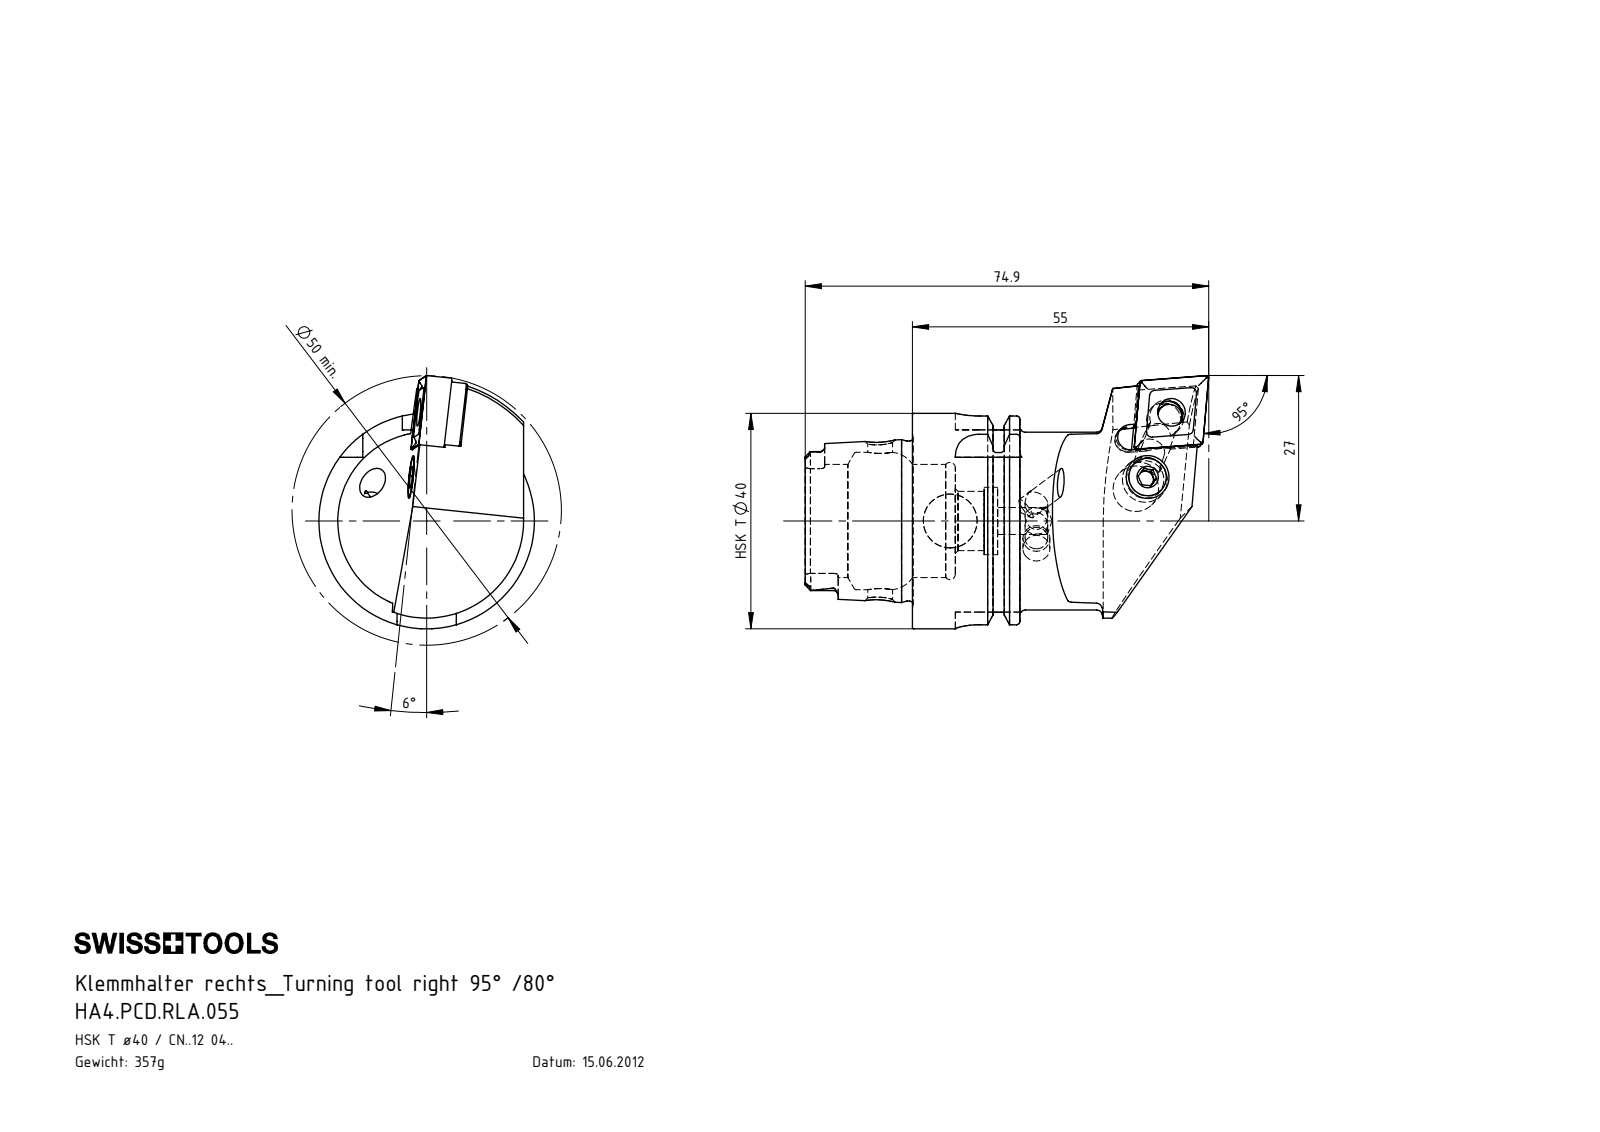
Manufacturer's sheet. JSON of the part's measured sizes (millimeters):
{"part_name": "HA4-PCD.RLA.055; WCD-ER1.101.000; WCD-ER4.101.017_A; WCD-ER3.101.000_A (+4 more)", "step_written_by": "SolidWorks 2012 (CONFIG_CONTROL_DESIGN)", "units": "millimeters", "bodies": {"solids": 8, "faces": 394, "planar": 124, "cylindrical": 110, "other": 160}, "overall_size": [74.9, 47, 40], "volume_mm3": 44610, "surface_area_mm2": 16279, "round_holes": [[4.2, 2], [4, 1], [4.6, 1], [5, 1], [5.16, 1], [6.4, 1], [7, 1], [8.4, 1], [10, 1], [11, 1], [12.5, 1], [21, 1]], "round_bosses_or_shafts": [[40, 1], [34.75, 1], [33, 1], [29.71, 1], [8, 1], [7.9, 1], [6.4, 1], [5, 1]], "partial_cylinders_radius": [[0.9, 6], [0.4, 4], [1, 4], [1.88, 4], [4.5, 4], [2.5, 2], [0.8, 1], [2.1, 1]], "face_to_face_distances": [4.46, 7.95, 19.95, 12, 3.18, 7.64, 19.9, 27.85, 39.85, 35.7], "hole_center_spacings": [12.8, 12.86]}
